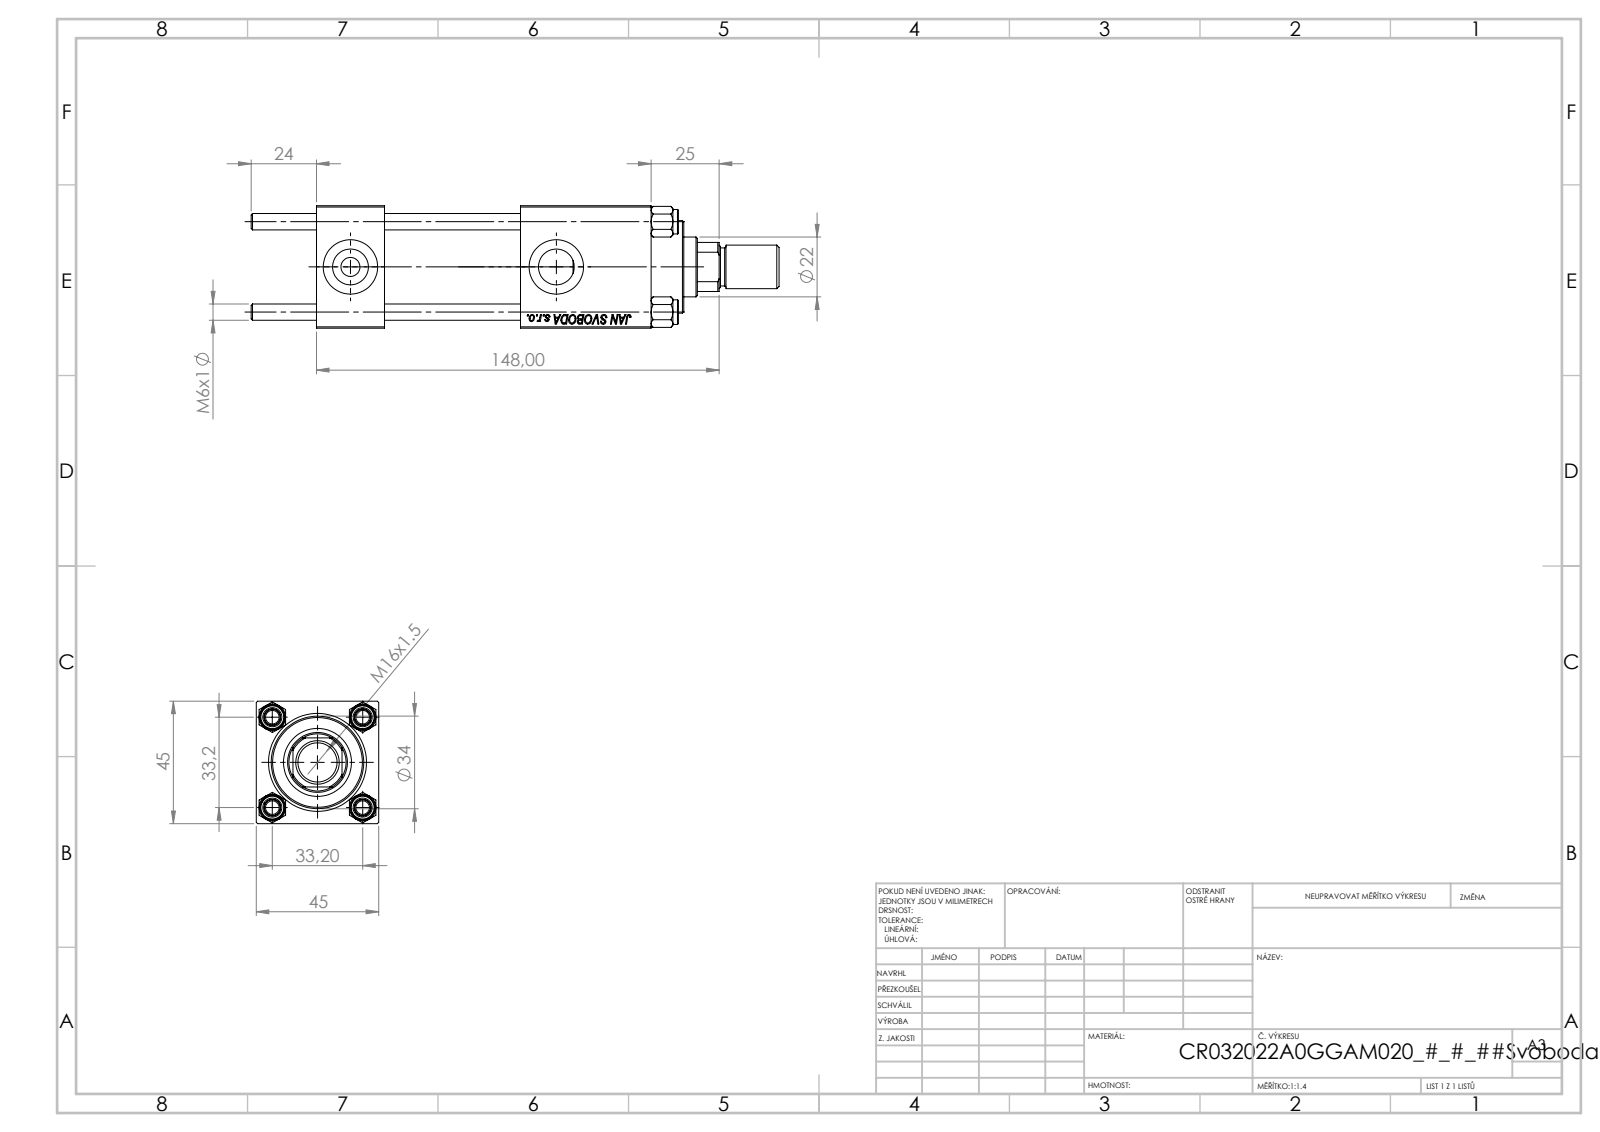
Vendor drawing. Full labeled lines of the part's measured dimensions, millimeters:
Part name (STEP PRODUCT): NUT_M5; CR025_012_A_0_G_A_G_M_020_+#_##_TYCINKA; V215CR_VCP; ROD_END_AH (+2 more)
STEP written by: SolidWorks 2019 (CONFIG_CONTROL_DESIGN)
Units: millimetres
Bodies: 12 solids, 1146 faces (521 planar, 83 cylindrical, 542 other)
Overall size (bounding box): 194 × 45 × 45
Volume: 218 502 mm³ · Surface area: 78 566 mm²
Round holes (diameter × count): ⌀6 ×4, ⌀7 ×2, ⌀13.16 ×2, ⌀20 ×2, ⌀10.5 ×1, ⌀22 ×1, ⌀24 ×1, ⌀25 ×1, ⌀32 ×1, ⌀33 ×1
Round bosses / shafts (diameter × count): ⌀9 ×4, ⌀38 ×1, ⌀34 ×1, ⌀16 ×1, ⌀14 ×1
Partial cylindrical surfaces — rounded edges, fillets, slot ends (radius × count): R10.5 ×1
Main face-to-face distances: 45, 25, 123, 50, 75, 98, 48, 94.3, 69.3, 19.3
Hole centre spacings: 23.48, 33.2, 46.95, 75.66
